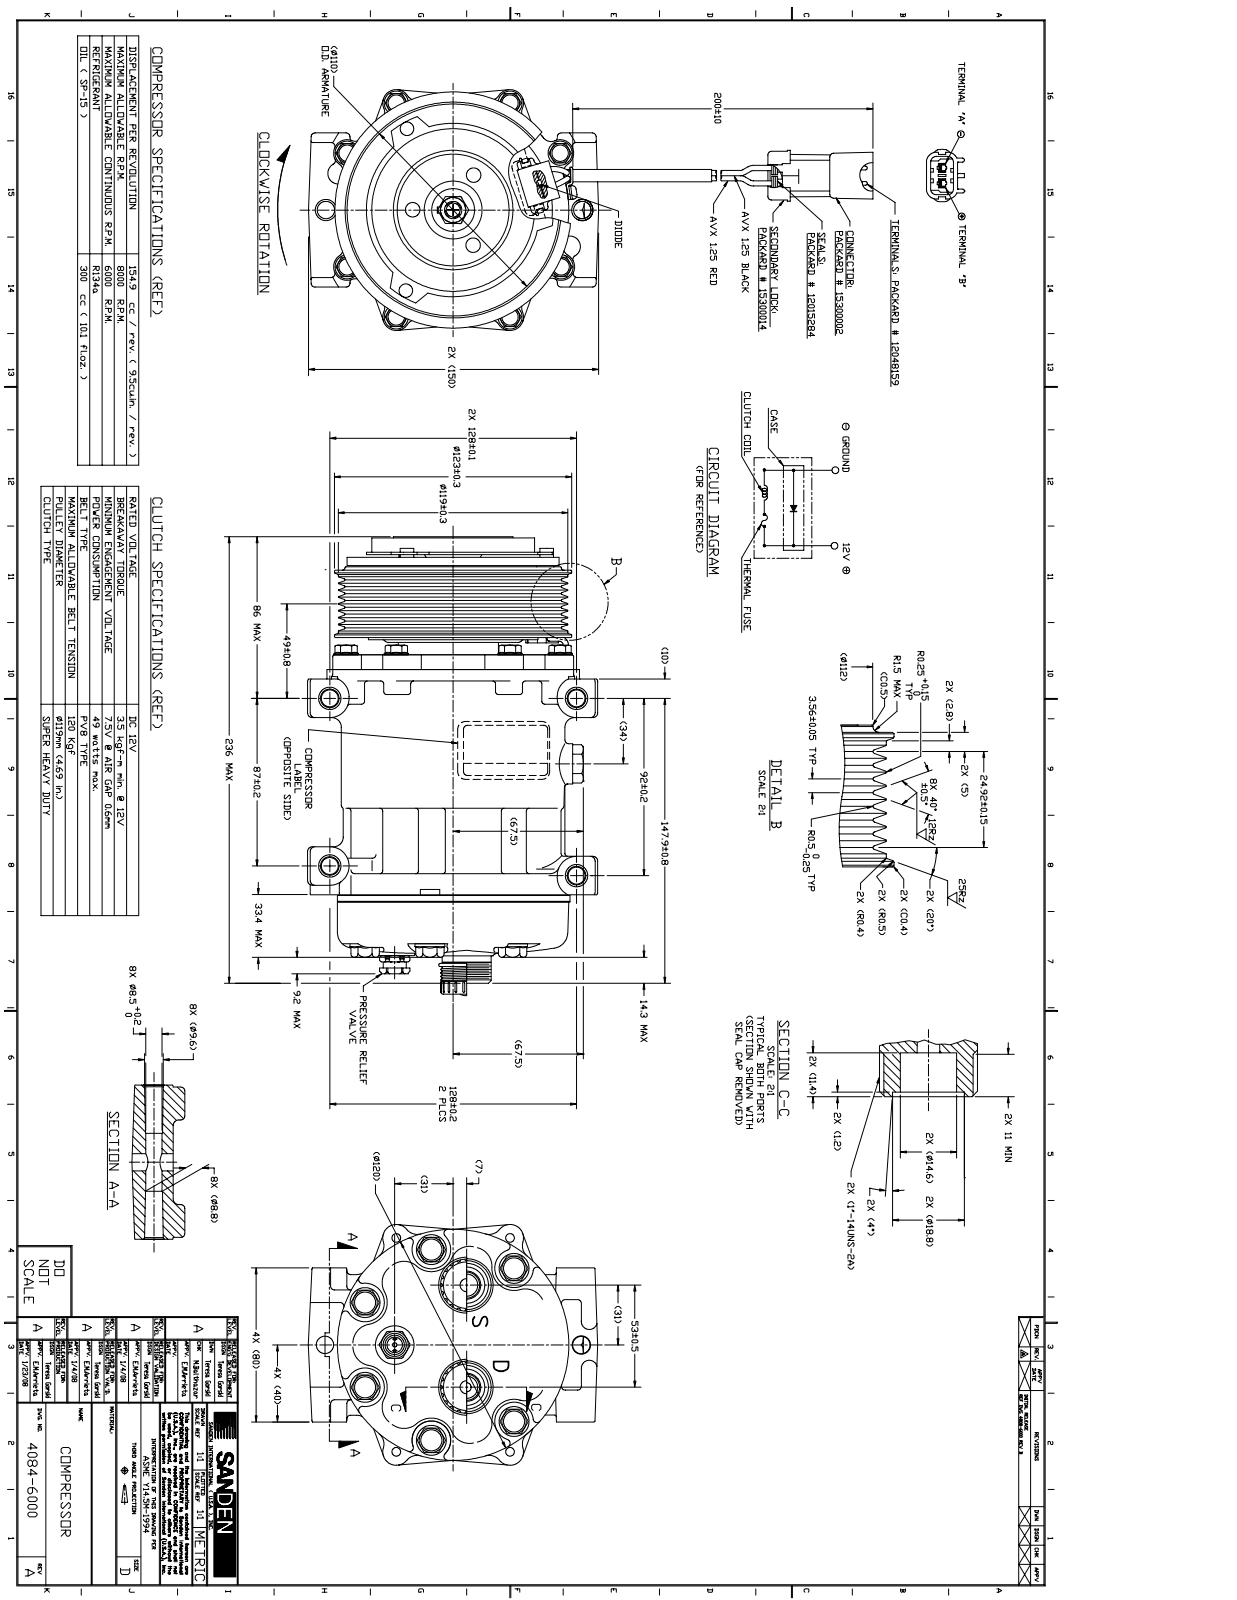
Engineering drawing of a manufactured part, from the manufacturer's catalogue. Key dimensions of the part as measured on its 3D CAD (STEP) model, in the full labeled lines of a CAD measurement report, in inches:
Part name (STEP PRODUCT): SANDEN_4084_REV_A_COMPR_AC
STEP written by: SolidWorks 2007 (CONFIG_CONTROL_DESIGN)
Units: inches
Bodies: 1 solid, 2313 faces (644 planar, 592 cylindrical, 1077 other)
Overall size (bounding box): 13.264 × 9.226 × 4.921
Volume: 136 in³ · Surface area: 384 in²
Round holes (diameter × count): ⌀0.344 ×8, ⌀0.444 ×6, ⌀0.335 ×4, ⌀0.25 ×3, ⌀0.118 ×2, ⌀0.354 ×2, ⌀0.472 ×2, ⌀0.575 ×2, ⌀0.138 ×1, ⌀0.14 ×1, ⌀0.256 ×1, ⌀0.327 ×1
Round bosses / shafts (diameter × count): ⌀0.492 ×8, ⌀0.106 ×8, ⌀0.315 ×4, ⌀0.276 ×4, ⌀4.724 ×2, ⌀1.039 ×2, ⌀1 ×2, ⌀0.787 ×2
Partial cylindrical surfaces — rounded edges, fillets, slot ends (radius × count): R0.02 ×46, R0.079 ×44, R0.276 ×32, R0.118 ×27, R0.098 ×18, R0.197 ×18, R0.394 ×14, R0.059 ×13
Main face-to-face distances: 0.209, 1.801, 0.024, 1.824, 2.009, 0.185, 0.236, 0.26, 1.565, 0.445
Hole centre spacings: 2.474, 3.5, 1.239, 1.448, 2.323, 2.626, 4.366, 4.37
